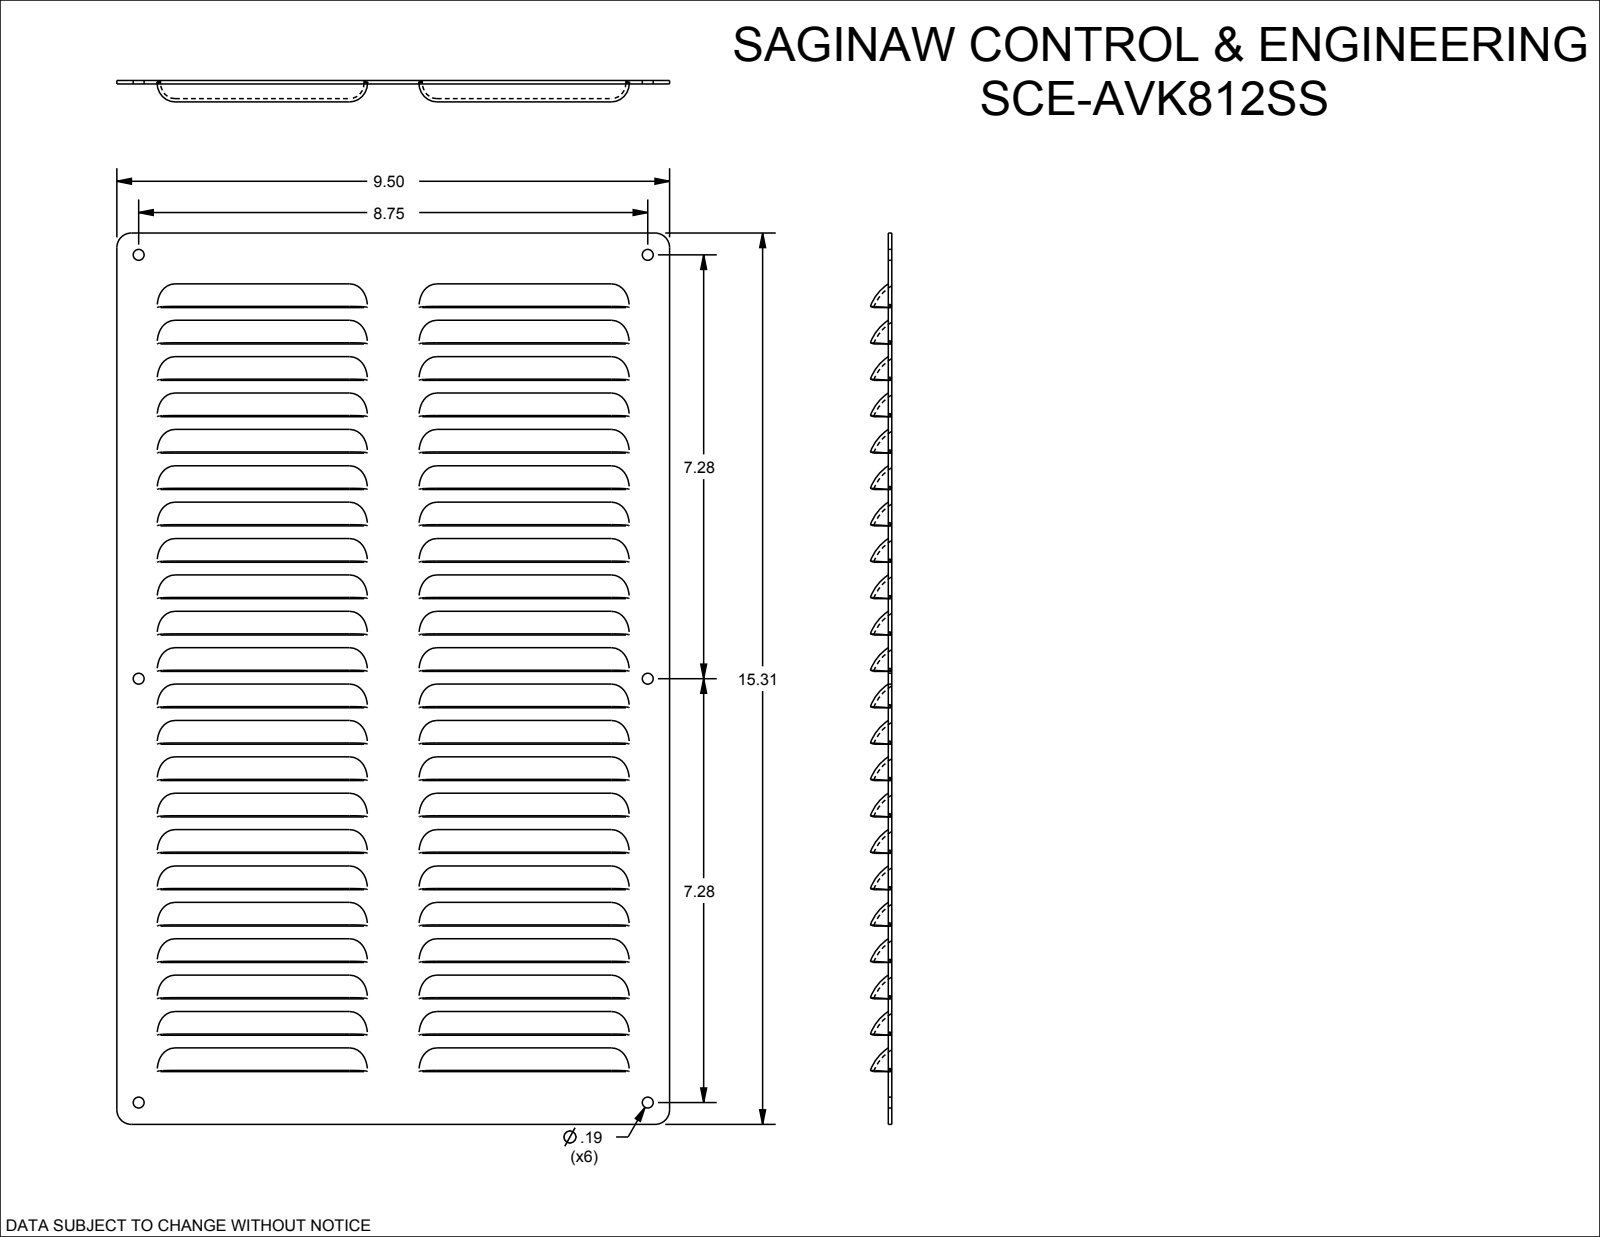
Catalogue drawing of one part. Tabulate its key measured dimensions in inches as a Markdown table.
| quantity | value |
| --- | --- |
| part name | SCE-AVK812SS |
| STEP written by | SolidWorks 2019 (CONFIG_CONTROL_DESIGN) |
| units | inches |
| bodies | 1 solid, 638 faces (94 planar, 104 cylindrical, 440 other) |
| overall size | 15.313 × 9.5 × 0.48 |
| volume | 9.873 in³ |
| surface area | 352.5 in² |
| round holes (diameter × count) | 0.187 × 6 |
| partial cylindrical surfaces (radius × count) | 0.74 × 22, 0.8 × 22, 0.25 × 4 |
| main face-to-face distances | 0.06, 1.171, 1.25, 2.5, 2.343, 3.514, 3.75, 0.625, 1.875, 3.125 |
| hole center spacings | 7.281, 11.383, 8.75, 14.562, 16.989 |
